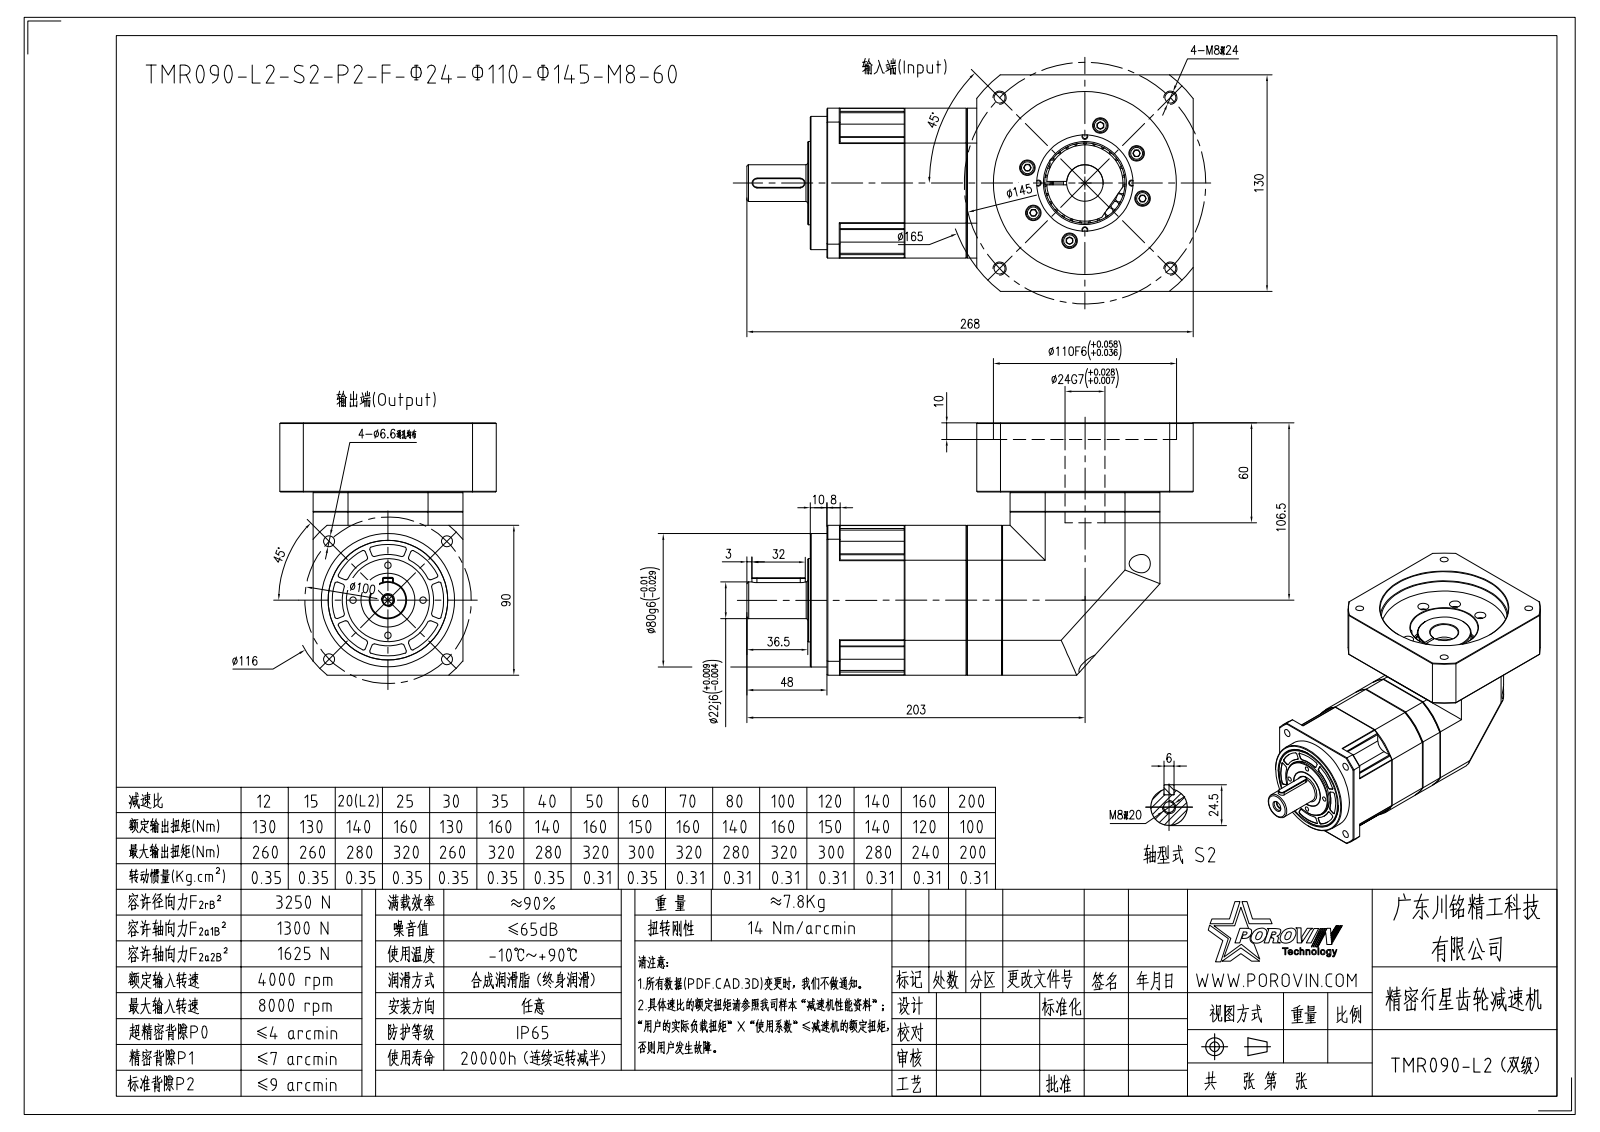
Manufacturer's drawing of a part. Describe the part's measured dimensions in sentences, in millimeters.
The part is named "HEXAGON_SOCKET_HEAD_CAP_SC-8126; SPRING_LOCK_WASHERS--NORM-18920; TM90_D110-M8-145F10001; TMR90240001 (+8 more)". Its 3-D file was written by "CREO PARAMETRIC BY PTC INC, 2020053 (CONFIG_CONTROL_DESIGN)". It is 43 solids with 1291 faces: 519 planar, 549 cylindrical and 223 other. Overall it measures 268 by 151.5 by 130 millimeters. Its volume is 1 906 000 cubic millimeters and its surface area 276 336 square millimeters. Round holes: 12 of diameter 5.4, 12 of diameter 9.5, 10 of diameter 6.6, 7 of diameter 4.2, 6 of diameter 5.5, 5 of diameter 6.5, 5 of diameter 6.8, 4 of diameter 4, 4 of diameter 6.68, 4 of diameter 11, 1 of diameter 5, 1 of diameter 8.4. Round bosses or shafts: 12 of diameter 8.5, 12 of diameter 8, 12 of diameter 5, 4 of diameter 10, 4 of diameter 9.88, 4 of diameter 6, 1 of diameter 80, 1 of diameter 55. Partial cylindrical surfaces (rounded edges, fillets, slot ends): 92 of radius 1, 4 of radius 7.5, 3 of radius 51, 2 of radius 3, 1 of radius 4, 1 of radius 5.25, 1 of radius 50.25, 1 of radius 58. The main face-to-face distances are 20, 110, 90, 41.5, 21.5, 12, 53.5, 21.3, 37.5, 58.8. The hole center spacings are 35.75, 27.36, 38.16, 44, 66.06, 66.53, 88.75, 13.64.
